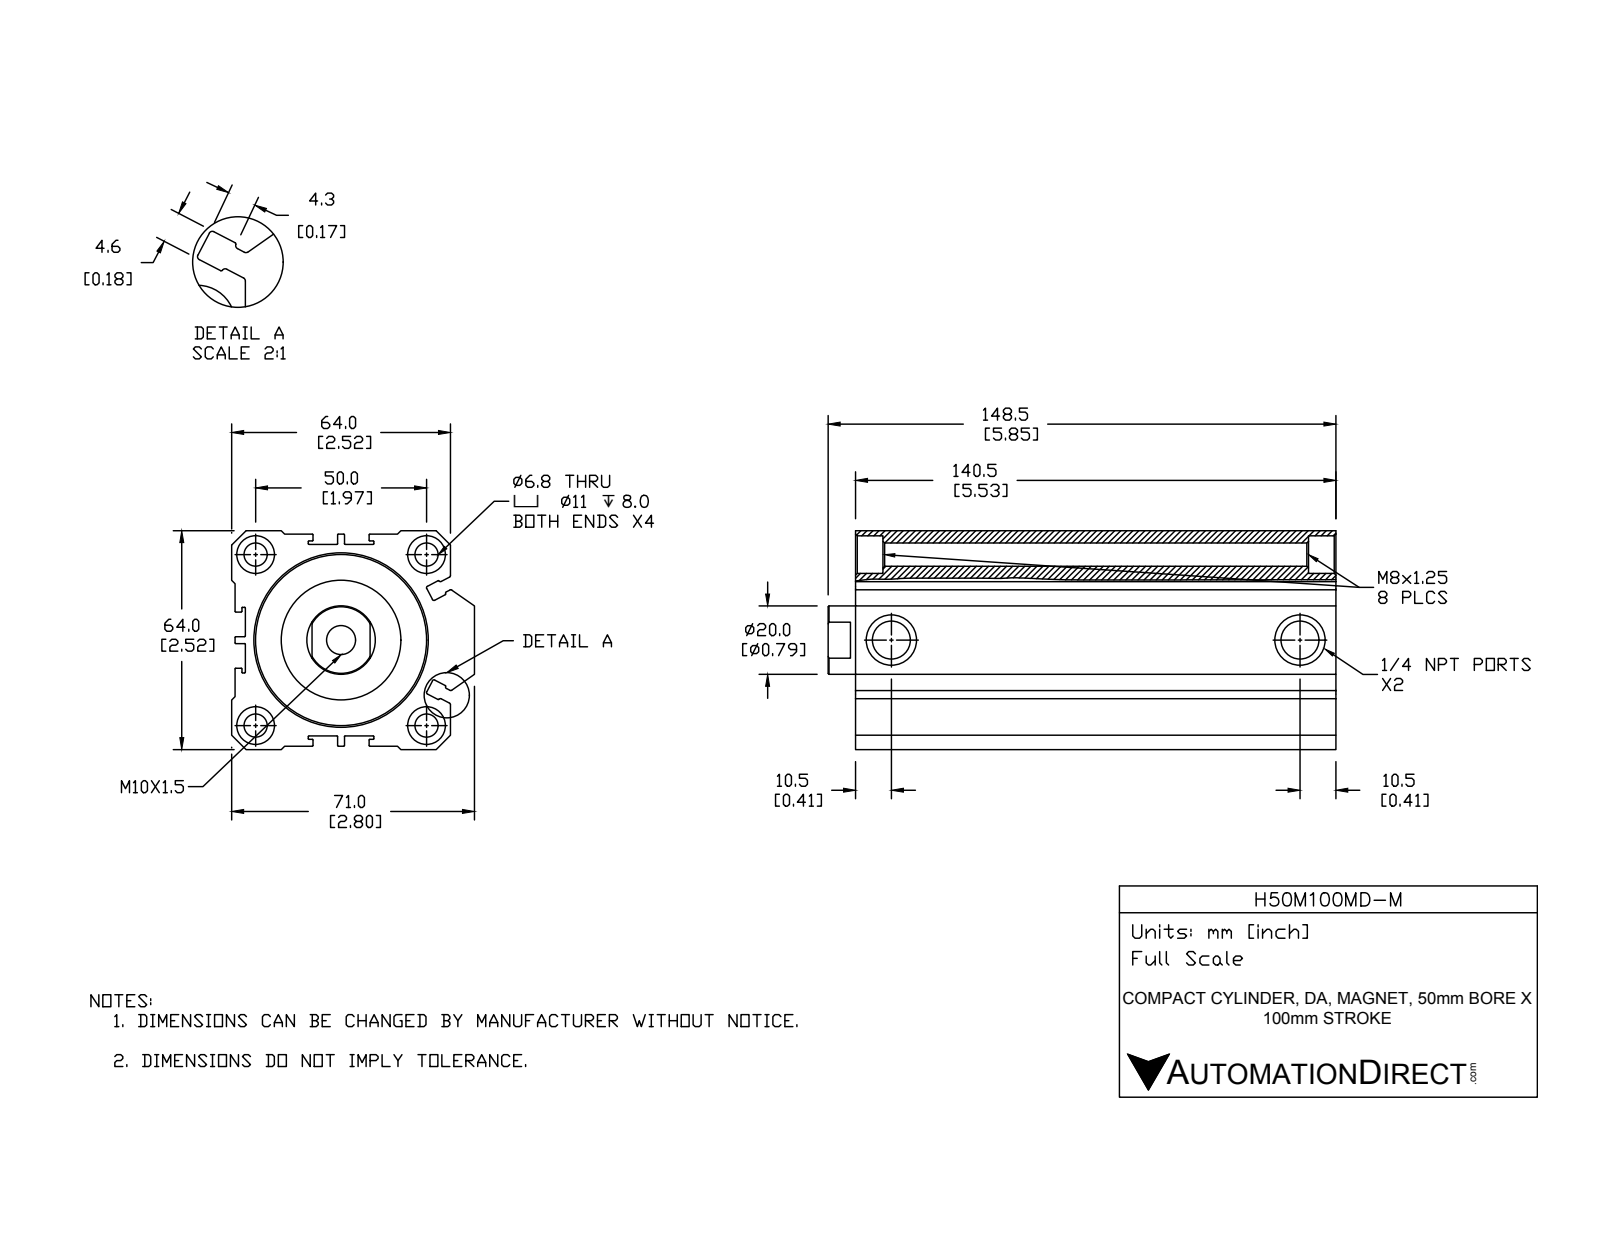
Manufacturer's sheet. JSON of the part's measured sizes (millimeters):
{"part_name": "H50M100MD-M-PISTON; H50M100MD-M-BODY; H50M100MD-M", "step_written_by": "SolidWorks 2015 (CONFIG_CONTROL_DESIGN)", "units": "millimeters", "bodies": {"solids": 2, "faces": 255, "planar": 99, "cylindrical": 103, "other": 53}, "overall_size": [148.5, 71, 64], "volume_mm3": 350647, "surface_area_mm2": 108090, "round_holes": [[6.8, 4], [11, 4], [11.13, 2], [8.5, 1], [20, 1], [36, 1], [50, 1]], "round_bosses_or_shafts": [[35, 1], [31, 1]], "partial_cylinders_radius": [[0.2, 40], [0.5, 12]], "face_to_face_distances": [4, 1, 3, 63, 60, 64, 59, 7, 30, 2], "hole_center_spacings": [35.36, 50, 70.71, 119.5]}
